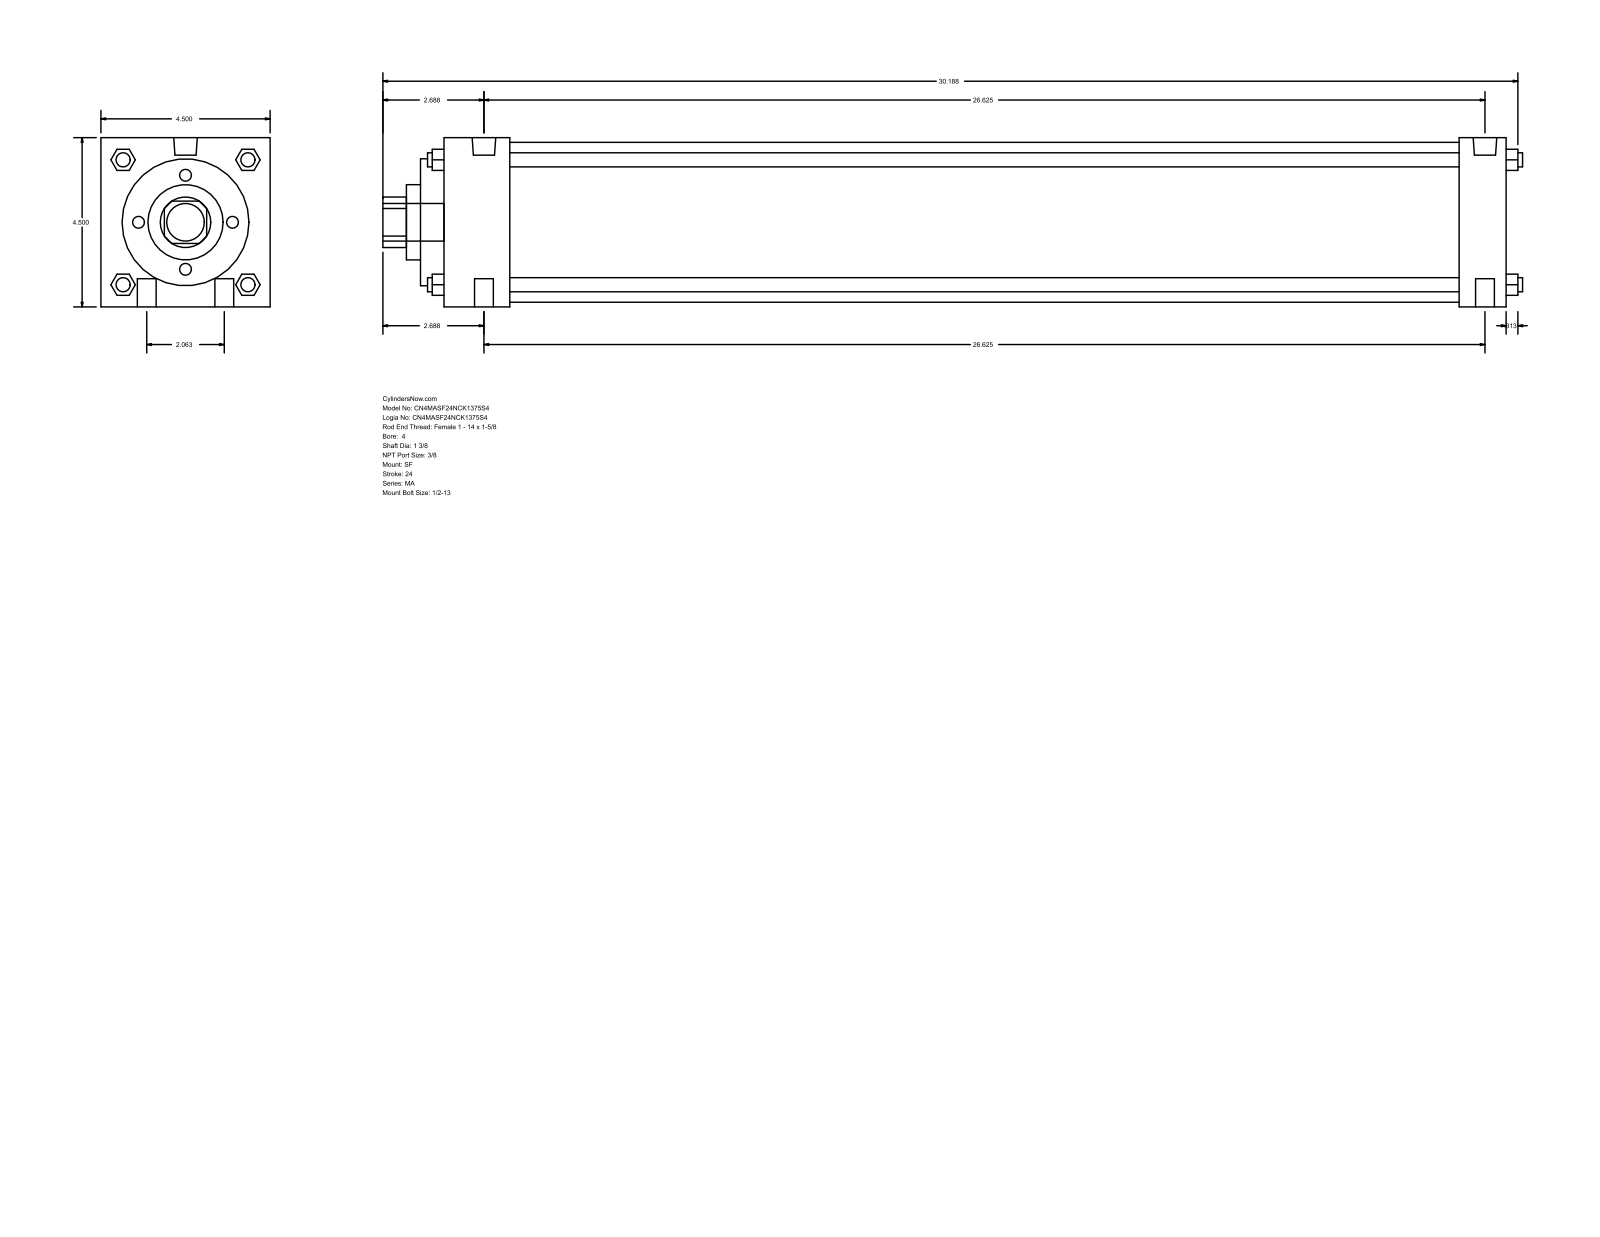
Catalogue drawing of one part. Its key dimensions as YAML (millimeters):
part_name: "MA_SF__0400_1.375"
step_written_by: "GSSL Pune (CONFIG_CONTROL_DESIGN)"
units: millimeters
bodies: {solids: 0, faces: 126, planar: 95, cylindrical: 31, other: 0}
overall_size: [769.94, 114.3, 114.3]
round_holes:
  - {diameter: 34.92, count: 1}
  - {diameter: 50.8, count: 1}
  - {diameter: 85.72, count: 1}
  - {diameter: 107.95, count: 1}
round_bosses_or_shafts:
  - {diameter: 12.7, count: 4}
  - {diameter: 9.53, count: 4}
  - {diameter: 15.93, count: 2}
  - {diameter: 11.11, count: 2}
  - {diameter: 25.4, count: 1}
partial_cylinders:
  - {radius: 17.06, count: 1}
face_to_face_distances: [114.3, 717.56, 15.87, 733.43, 701.68, 685.81, 31.75, 60.32, 44.45, 641.36]
